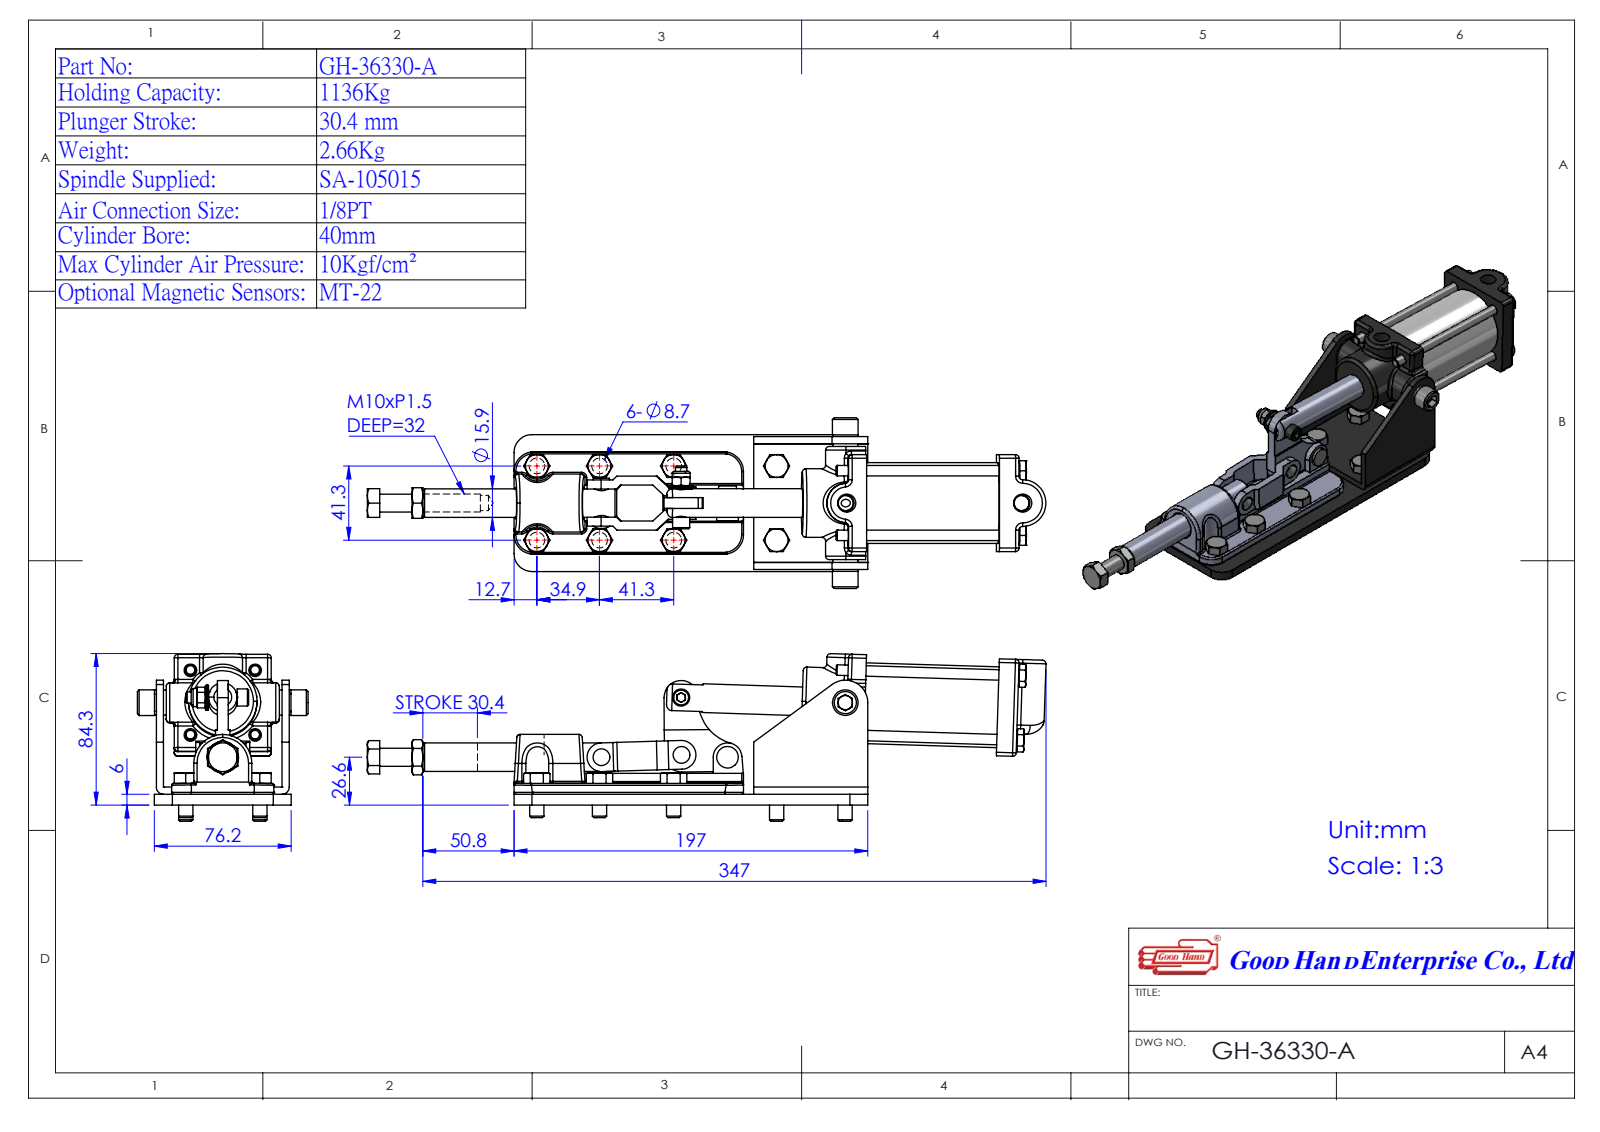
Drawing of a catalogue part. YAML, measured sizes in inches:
part_name: "GH-36330-A(簡化); Group6^GH-36330-A(簡化); Group2^GH-36330-A(簡化); 0303004-1^GH-36330-A(簡化) (+4 more)"
step_written_by: "SolidWorks 2016 (AUTOMOTIVE_DESIGN)"
units: inches
bodies: {solids: 8, faces: 885, planar: 343, cylindrical: 262, other: 280}
overall_size: [14.983, 3.742, 3.669]
volume: 26.51
surface_area: 229.1
round_holes:
  - {diameter: 0.236, count: 4}
  - {diameter: 0.311, count: 2}
  - {diameter: 0.197, count: 1}
  - {diameter: 0.248, count: 1}
  - {diameter: 0.281, count: 1}
  - {diameter: 0.291, count: 1}
  - {diameter: 0.315, count: 1}
  - {diameter: 0.335, count: 1}
  - {diameter: 0.394, count: 1}
  - {diameter: 0.626, count: 1}
  - {diameter: 0.63, count: 1}
  - {diameter: 1.654, count: 1}
round_bosses_or_shafts:
  - {diameter: 0.313, count: 10}
  - {diameter: 0.25, count: 5}
  - {diameter: 0.438, count: 2}
  - {diameter: 0.394, count: 2}
  - {diameter: 0.354, count: 2}
  - {diameter: 1.693, count: 1}
  - {diameter: 1.654, count: 1}
  - {diameter: 1.504, count: 1}
partial_cylinders:
  - {radius: 0.079, count: 30}
  - {radius: 0.039, count: 16}
  - {radius: 0.433, count: 6}
  - {radius: 0.071, count: 4}
  - {radius: 0.118, count: 4}
  - {radius: 0.394, count: 4}
  - {radius: 0.315, count: 3}
  - {radius: 0.031, count: 2}
face_to_face_distances: [0.157, 0.236, 0.394, 2.756, 1.181, 1.457, 1.299, 1.142, 1.614, 2.598]
hole_center_spacings: [1.009, 1.256, 1.657, 1.756, 2.097, 2.765, 2.846, 3.667]
